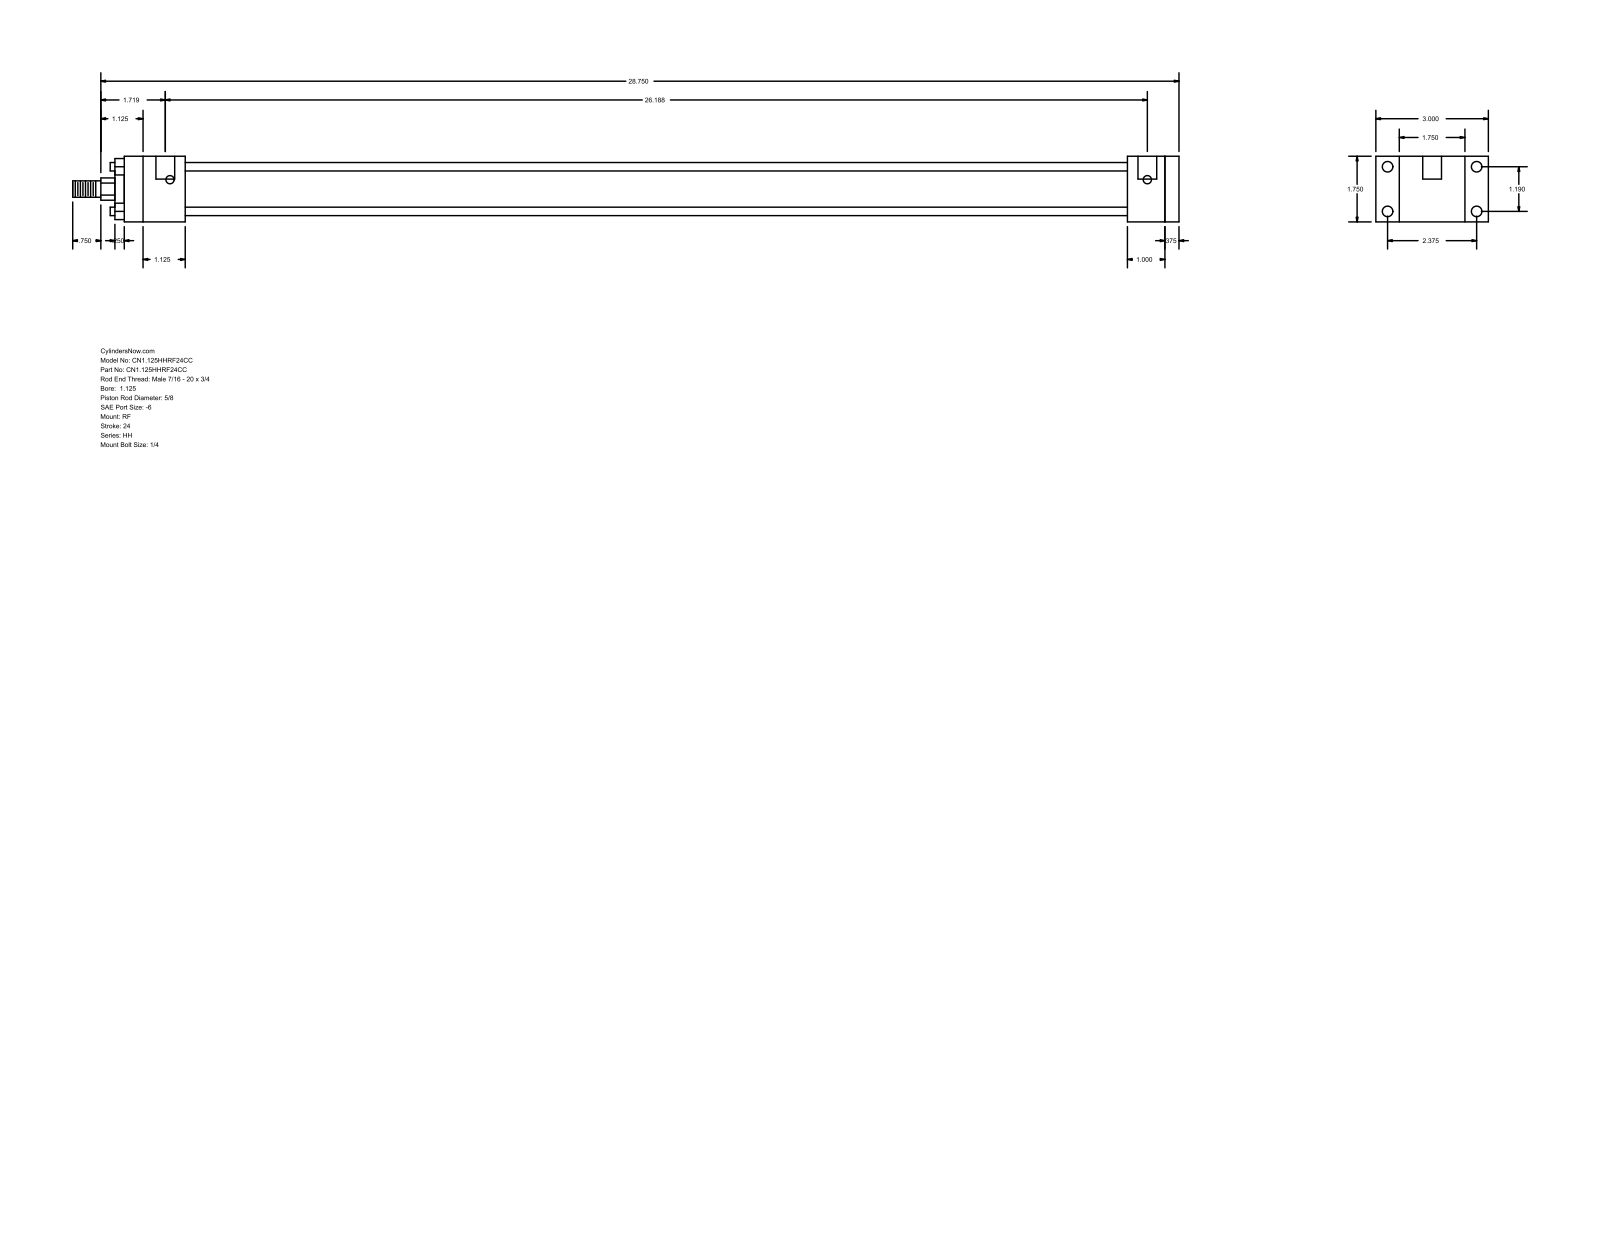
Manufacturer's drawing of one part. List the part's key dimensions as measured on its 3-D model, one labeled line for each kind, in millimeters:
Part name (STEP PRODUCT): HH_RF__0112_0.625
STEP written by: GSSL Pune (CONFIG_CONTROL_DESIGN)
Units: millimetres
Bodies: 0 solids, 92 faces (64 planar, 28 cylindrical, 0 other)
Overall size (bounding box): 749.3 × 76.2 × 44.45
Round holes (diameter × count): ⌀5.56 ×4, ⌀7.14 ×4, ⌀12.7 ×2
Round bosses / shafts (diameter × count): ⌀5.71 ×4, ⌀34.92 ×1, ⌀28.57 ×1, ⌀15.88 ×1, ⌀11.11 ×1
Partial cylindrical surfaces — rounded edges, fillets, slot ends (radius × count): R7.54 ×1
Main face-to-face distances: 44.46, 9.52, 25.4, 15.87, 663.58, 673.1, 638.18, 34.92, 41.27, 679.45
Hole centre spacings: 30.22, 60.32, 67.47, 661.99, 3.17, 665.16
